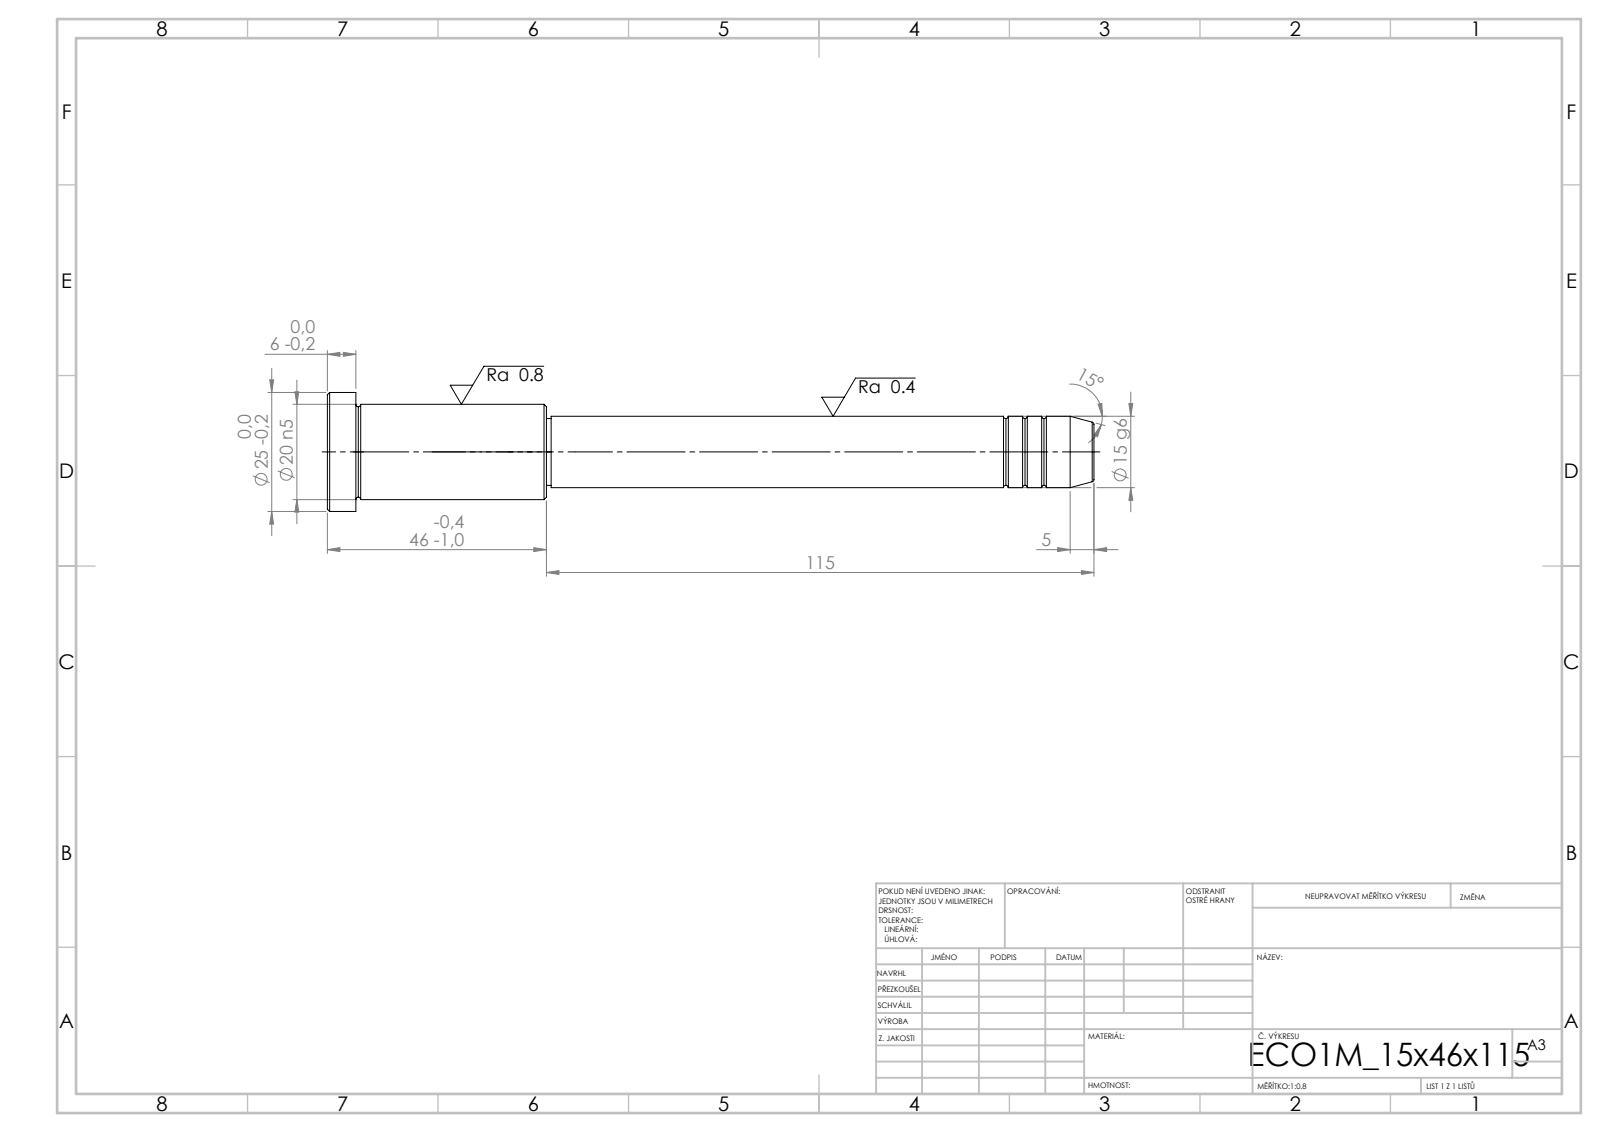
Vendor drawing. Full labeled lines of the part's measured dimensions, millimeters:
STEP written by: SolidWorks 2019 (CONFIG_CONTROL_DESIGN)
Units: millimetres
Bodies: 1 solid, 43 faces (5 planar, 14 cylindrical, 24 other)
Overall size (bounding box): 161 × 25 × 25
Volume: 35 566 mm³ · Surface area: 9 414 mm²
Round bosses / shafts (diameter × count): ⌀25 ×1, ⌀20 ×1, ⌀15 ×1, ⌀14 ×1
Main face-to-face distances: 6, 40, 46, 115, 155, 161, 114, 1, 41, 47
